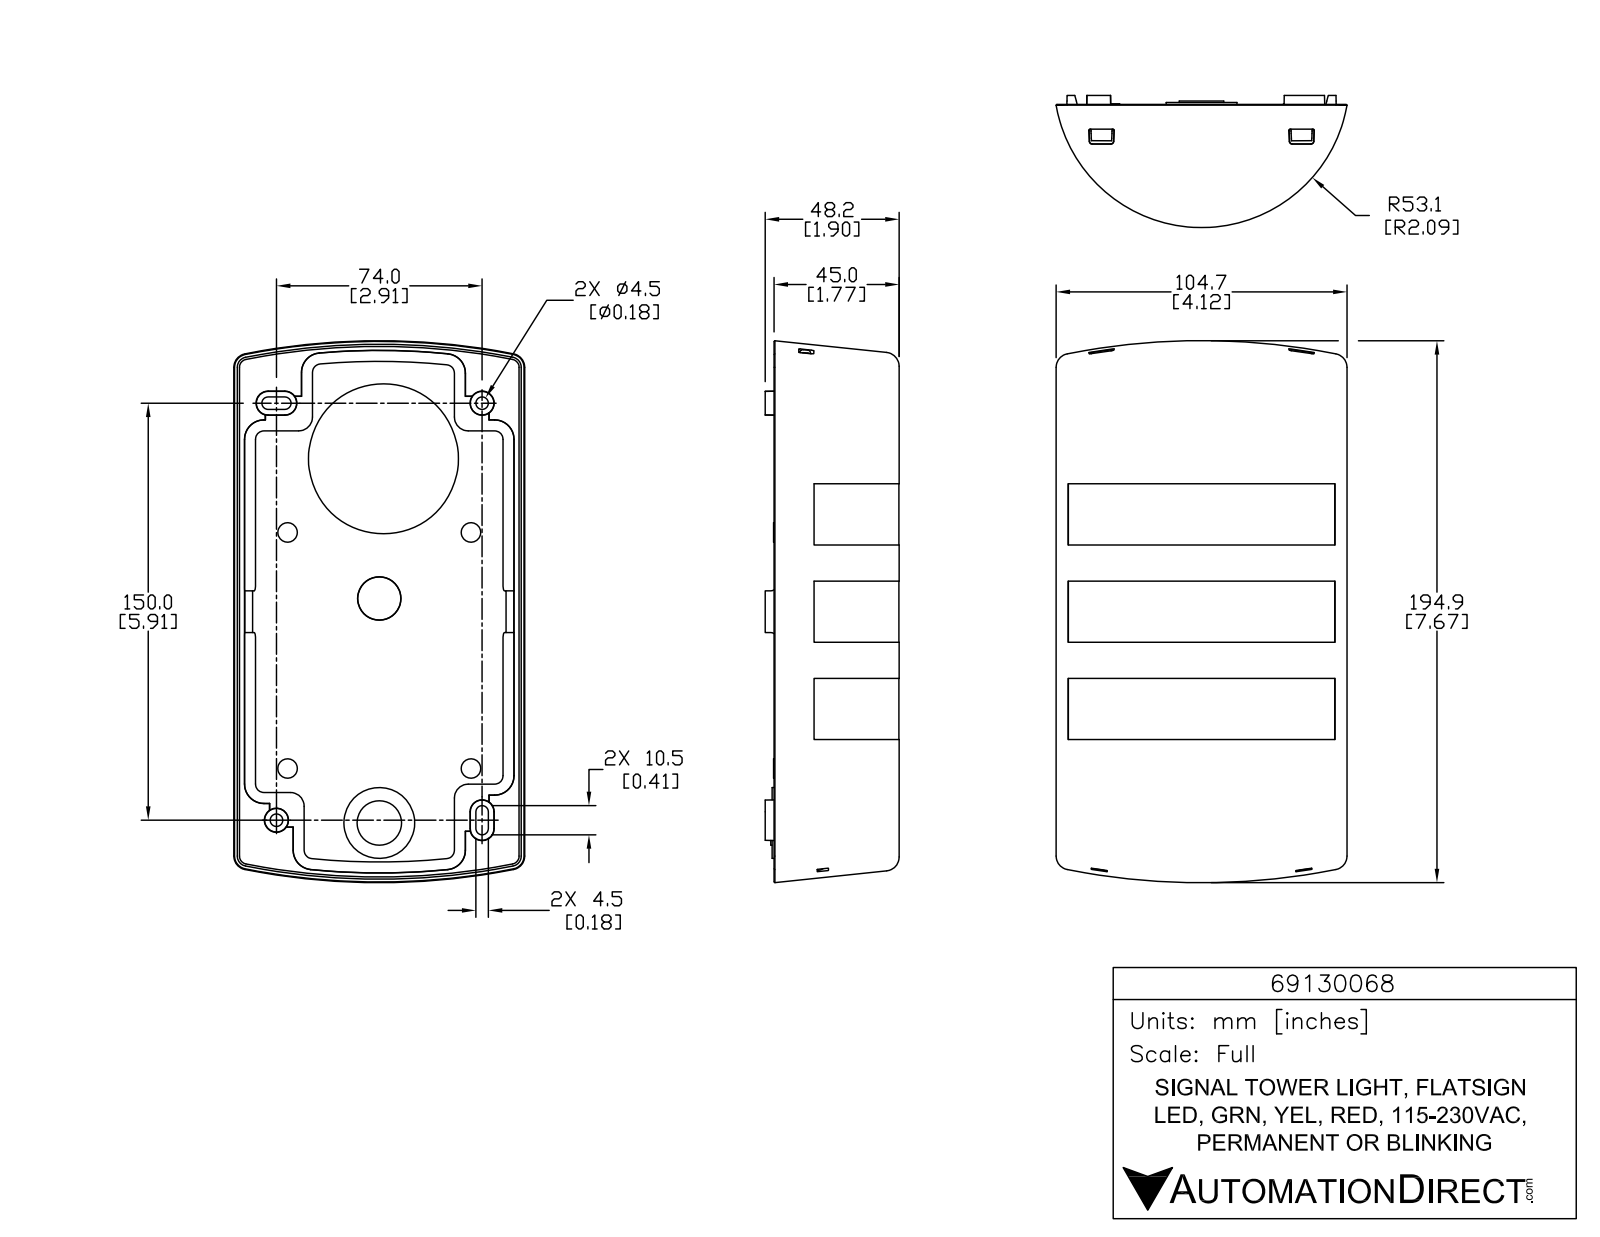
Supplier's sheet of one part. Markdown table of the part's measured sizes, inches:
| quantity | value |
| --- | --- |
| part name | 69130068 |
| STEP written by | SolidWorks 2017 (AUTOMOTIVE_DESIGN) |
| units | inches |
| bodies | 1 solid, 1074 faces (520 planar, 128 cylindrical, 426 other) |
| overall size | 7.675 × 4.122 × 1.901 |
| volume | 38.36 in³ |
| surface area | 92.68 in² |
| round holes (diameter × count) | 0.089 × 1 |
| round bosses / shafts (diameter × count) | 2.126 × 1, 1.004 × 1, 0.63 × 1, 0.514 × 1, 0.128 × 1 |
| partial cylindrical surfaces (radius × count) | 0.039 × 12, 0.012 × 4, 0.008 × 3, 0.008 × 2, 0.018 × 2, 0.019 × 2, 0.019 × 2, 0.02 × 2 |
| main face-to-face distances | 0.031, 0.079, 0.047, 0.11, 0.063, 0.157, 0.039, 0.02, 0.138, 0.118 |
